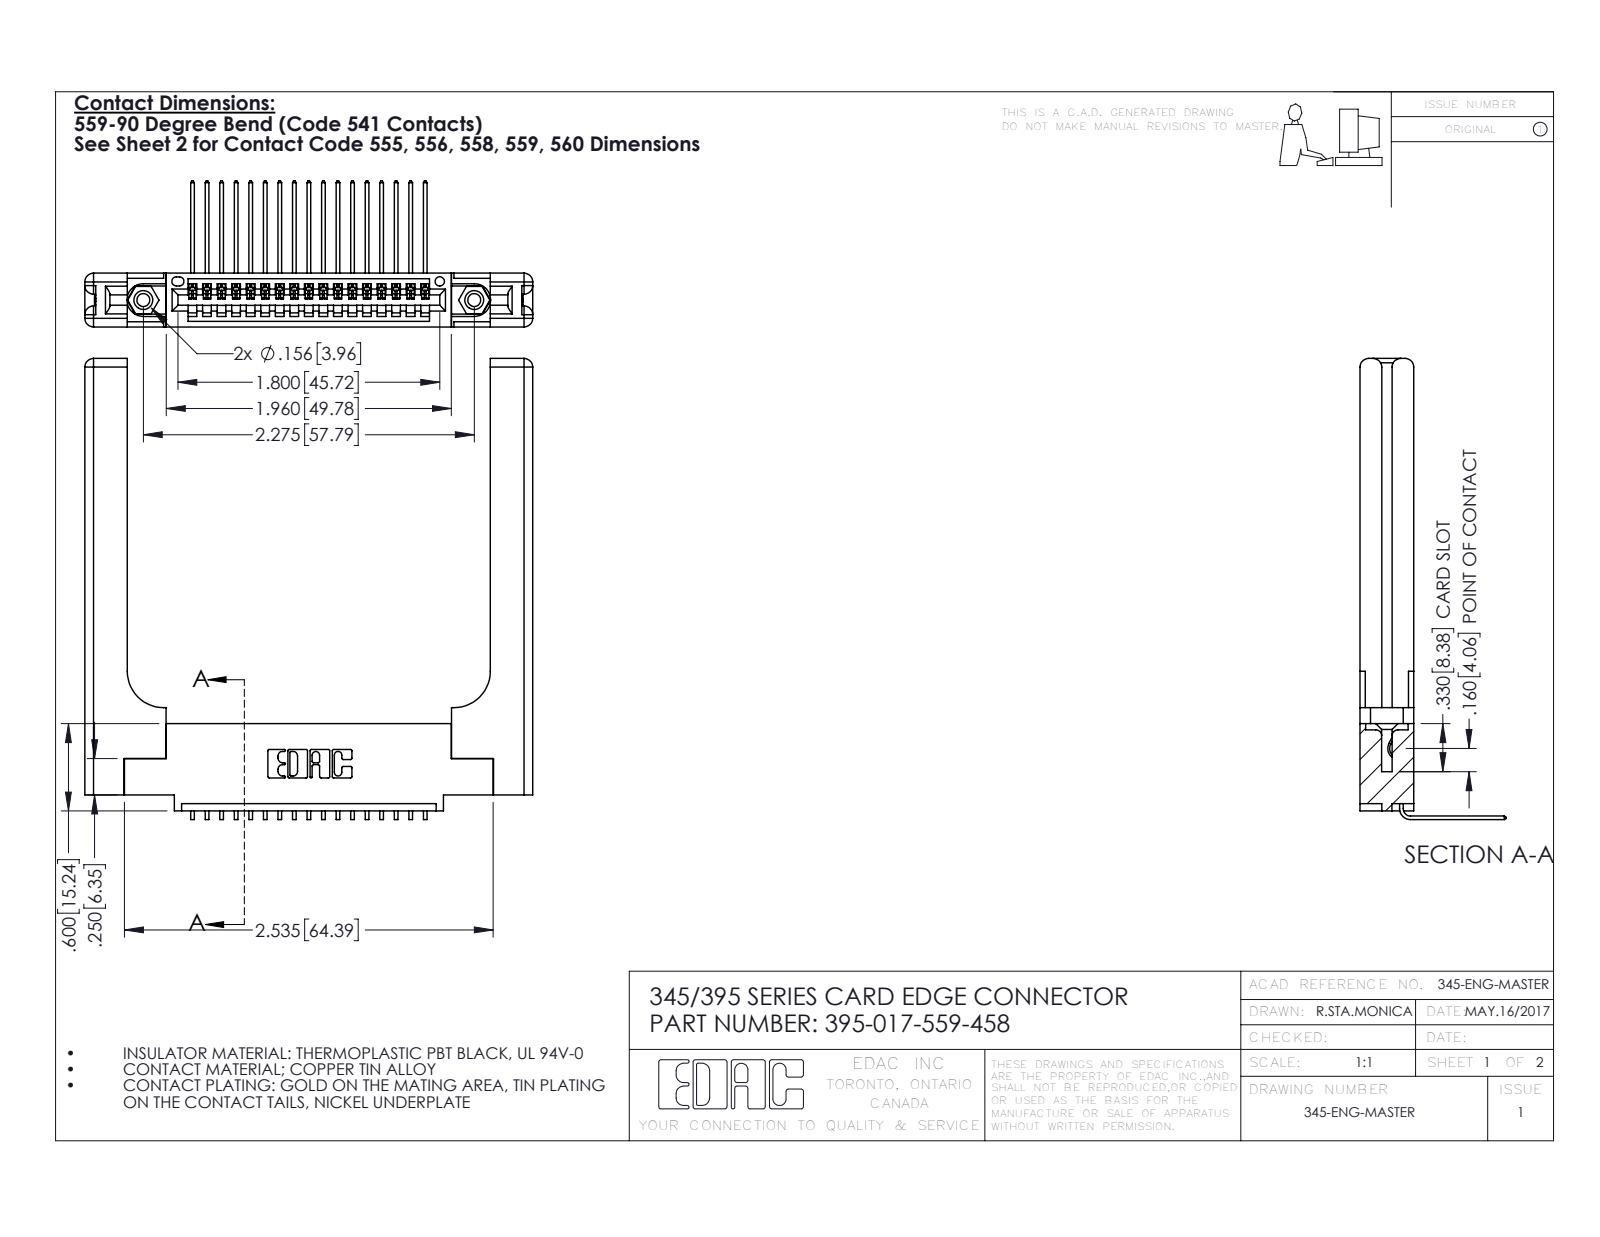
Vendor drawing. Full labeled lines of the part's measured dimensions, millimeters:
Part name (STEP PRODUCT): 345-250-001_345-250-001-102; 345-292-001_558 559 Tail - 1; 395-017-559-458; 345-220-058_345-220-058 (+1 more)
STEP written by: SolidWorks 2016 (CONFIG_CONTROL_DESIGN)
Units: millimetres
Bodies: 22 solids, 1406 faces (946 planar, 400 cylindrical, 60 other)
Overall size (bounding box): 80.5 × 78.2 × 25.5
Volume: 15 700 mm³ · Surface area: 14 950 mm²
Round holes (diameter × count): ⌀2.3 ×2, ⌀3.2 ×2, ⌀4 ×2, ⌀1.6 ×1
Round bosses / shafts (diameter × count): ⌀3.9 ×2
Partial cylindrical surfaces — rounded edges, fillets, slot ends (radius × count): R0.2 ×34, R0.3 ×22, R1.5 ×16, R0.2 ×6, R0.8 ×6, R0.7 ×3, R0.8 ×2, R0.8 ×2
Main face-to-face distances: 9.4, 1.8, 7.6, 3.8, 3.8, 2, 5.6, 2.5, 6.9, 0.6
Hole centre spacings: 6.9, 51.8, 57.8
